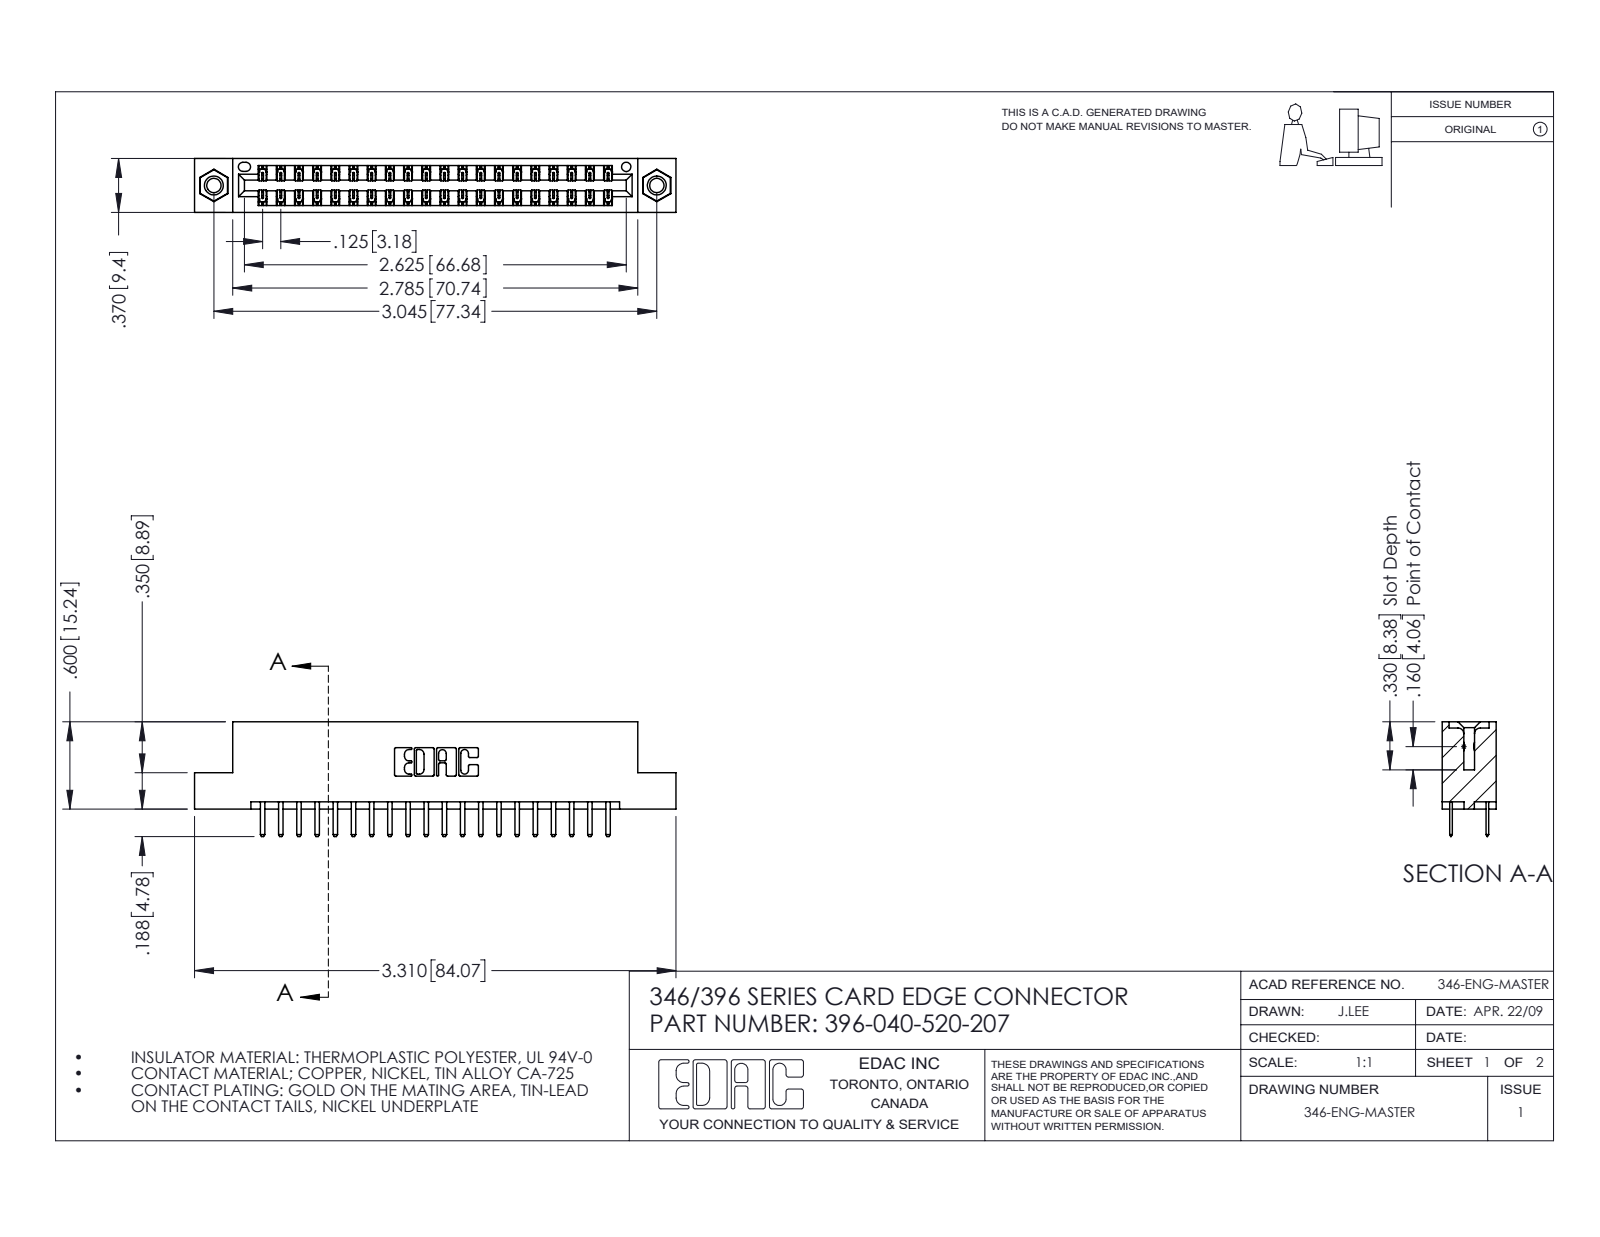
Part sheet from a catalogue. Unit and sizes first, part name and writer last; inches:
Units: inches
Overall size (bounding box): 3.31 × 0.788 × 0.37
Round holes (diameter × count): ⌀0.098 ×2, ⌀0.125 ×2, ⌀0.156 ×2, ⌀0.064 ×1
Round bosses / shafts (diameter × count): ⌀0.155 ×2
Partial cylindrical surfaces — rounded edges, fillets, slot ends (radius × count): R0.006 ×60, R0.01 ×44, R0.01 ×22, R0.007 ×6, R0.031 ×6, R0.026 ×3, R0.014 ×2, R0.022 ×2
Main face-to-face distances: 0.048, 0.322, 0.25, 0.37, 0.275, 0.072, 0.298, 0.025, 0.148, 0.222
Hole centre spacings: 0.246, 2.837, 3.045
Volume: 0.488 in³ · Surface area: 16.49 in²
Bodies: 43 solids, 2422 faces (1588 planar, 818 cylindrical, 16 other)
Part name (STEP PRODUCT): 345-292-001_345-293-120; 345-250-001_345-250-005-103; 346 Part_Flush Mounting Lugs - 0.156 Dia-TI; 396-040-520-207
STEP written by: SolidWorks 2016 (CONFIG_CONTROL_DESIGN)
